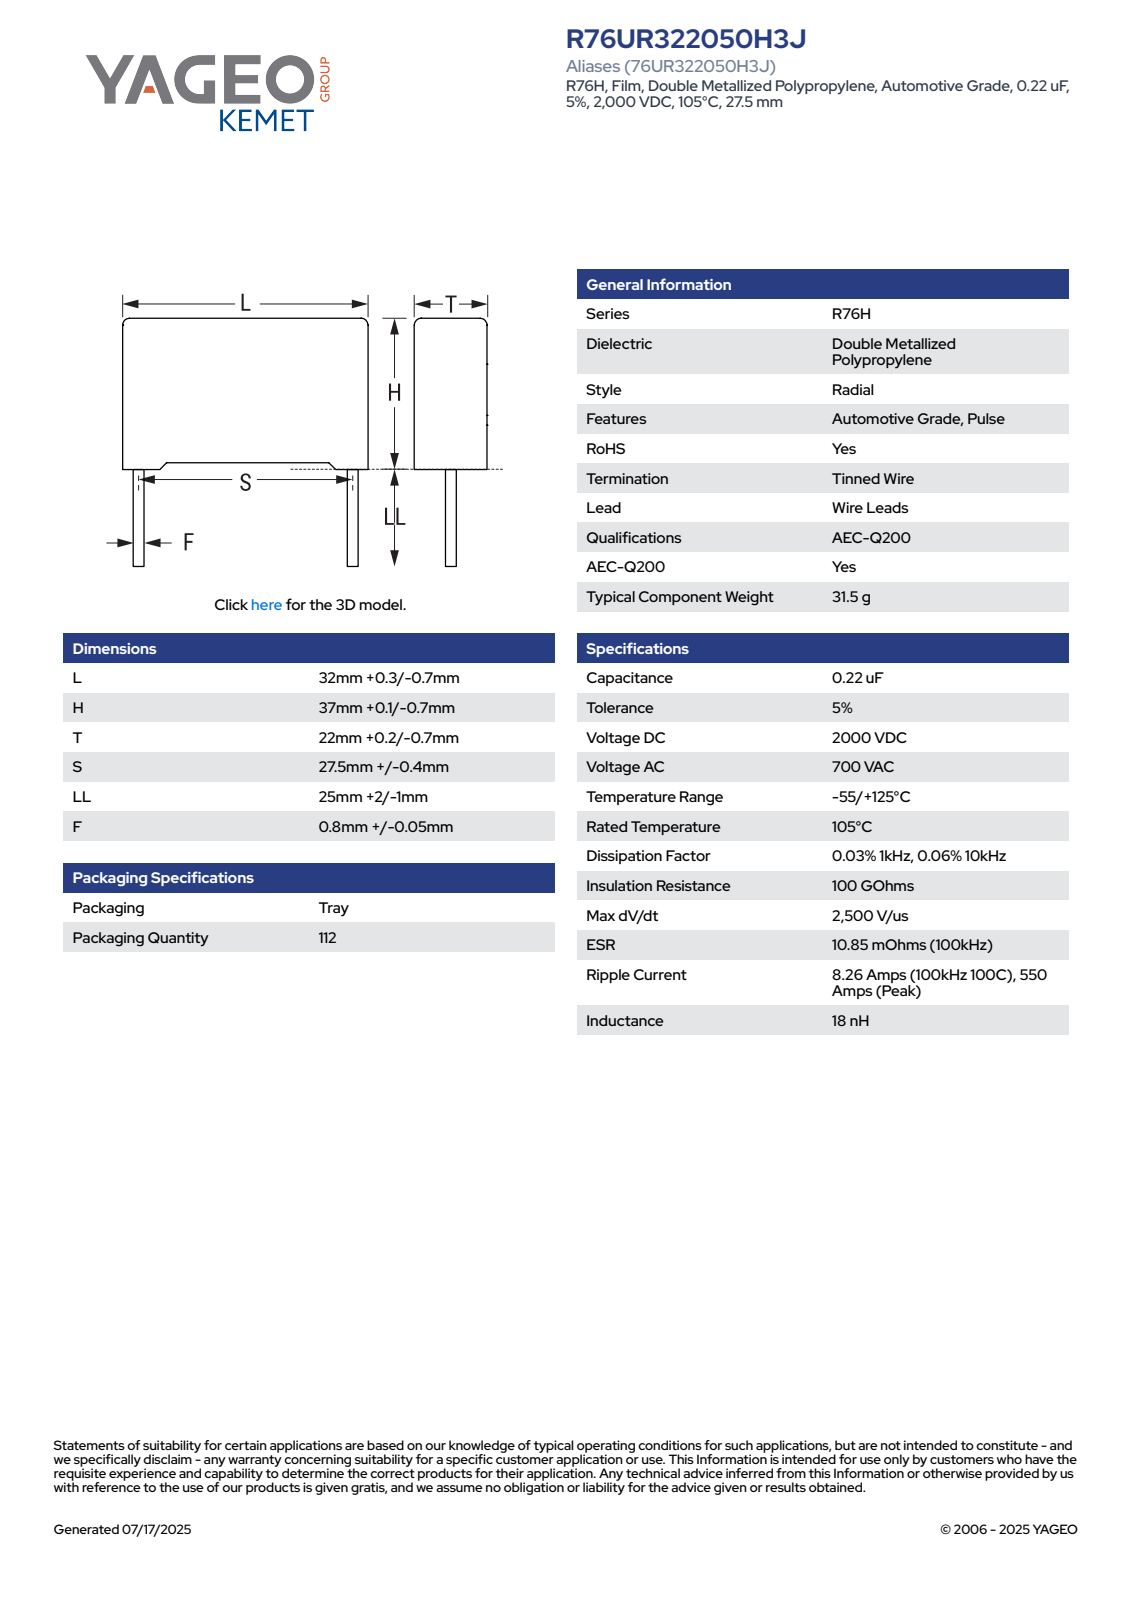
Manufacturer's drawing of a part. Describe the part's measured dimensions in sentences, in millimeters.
The part is named "CFR_RB2R76_32X37X22_L32.3H37.1T22.2S27.5LL27F0.85". Its 3-D file was written by "SolidWorks 2014 (AUTOMOTIVE_DESIGN)". It is 4 solids with 85 faces: 77 planar, 8 cylindrical and 0 other. Overall it measures 64.1 by 32.3 by 22.2 millimeters. Its volume is 25 866 cubic millimeters and its surface area 5 674 square millimeters. Round bosses or shafts: 2 of diameter 0.85. Partial cylindrical surfaces (rounded edges, fillets, slot ends): 4 of radius 0.5. The main face-to-face distances are 22.2, 32.3, 35.82, 0.53, 36.35, 0.75, 1.28, 37.1, 1.08, 31.22.
